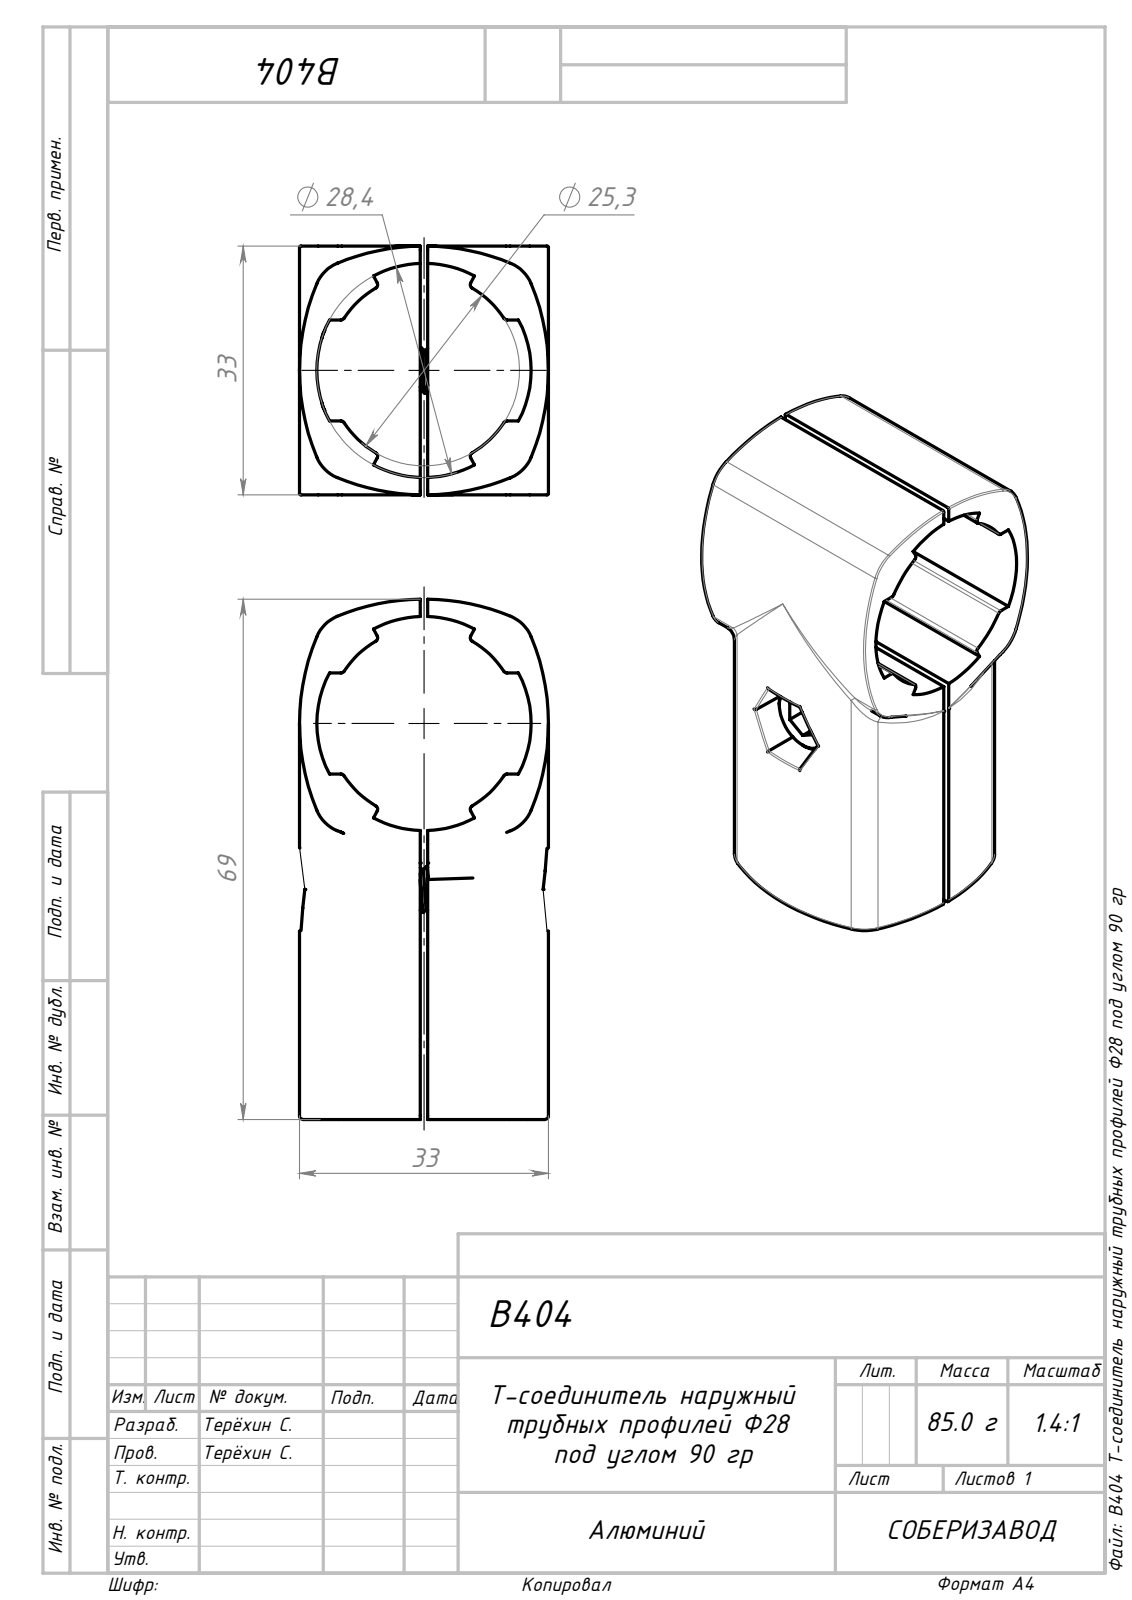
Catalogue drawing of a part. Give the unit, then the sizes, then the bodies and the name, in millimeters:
Units: millimetres
Overall size (bounding box): 69 × 33 × 32.99
Round holes (diameter × count): ⌀5.2 ×1, ⌀6.5 ×1, ⌀28.4 ×1
Round bosses / shafts (diameter × count): ⌀10 ×1, ⌀6 ×1
Partial cylindrical surfaces — rounded edges, fillets, slot ends (radius × count): R0.5 ×20, R1 ×16, R5 ×8, R30 ×8, R12.65 ×2, R14.2 ×1
Main face-to-face distances: 1, 6, 7, 10.28, 33, 13, 23, 13.38, 10, 45.81
Volume: 30 355 mm³ · Surface area: 17 813 mm²
Bodies: 4 solids, 365 faces (108 planar, 142 cylindrical, 115 other)
Part name (STEP PRODUCT): B404 Т-соединитель наружный трубных профилей Ф28 под углом 90 гр
STEP written by: SolidWorks 2022 (AUTOMOTIVE_DESIGN)
